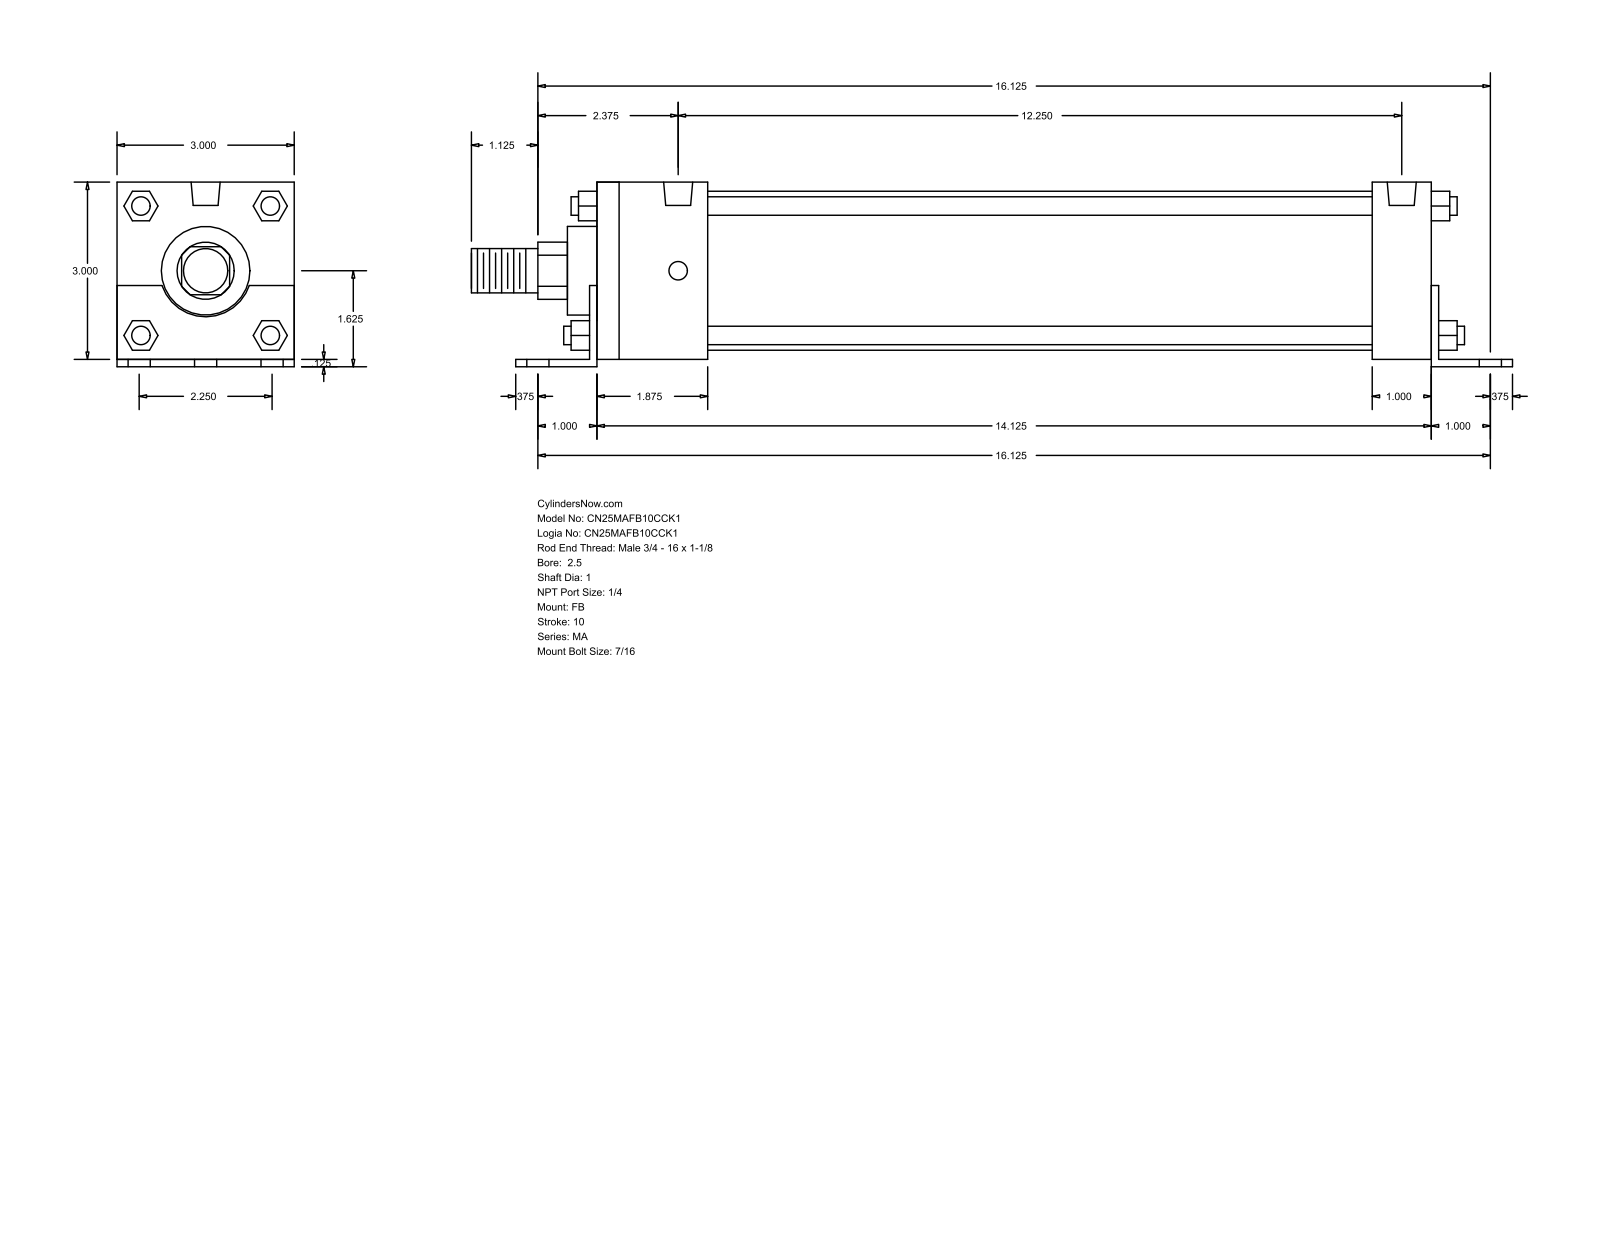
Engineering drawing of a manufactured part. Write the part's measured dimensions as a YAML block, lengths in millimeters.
part_name: "MA_FB__0250_1"
step_written_by: "GSSL Pune (CONFIG_CONTROL_DESIGN)"
units: millimeters
bodies: {solids: 0, faces: 140, planar: 105, cylindrical: 35, other: 0}
overall_size: [447.68, 79.38, 76.2]
round_holes:
  - {diameter: 11.11, count: 6}
  - {diameter: 7.94, count: 4}
  - {diameter: 12.49, count: 2}
round_bosses_or_shafts:
  - {diameter: 7.94, count: 4}
  - {diameter: 68.33, count: 1}
  - {diameter: 38.1, count: 1}
  - {diameter: 25.4, count: 1}
  - {diameter: 19.05, count: 1}
partial_cylinders:
  - {radius: 12.29, count: 1}
  - {radius: 19.81, count: 1}
face_to_face_distances: [76.2, 3.17, 79.37, 361.95, 358.78, 12.7, 50.8, 47.63, 311.15, 314.32]
hole_center_spacings: [28.57, 410.57, 409.57, 47.61, 57.14, 66.75, 311.15, 350.41]
